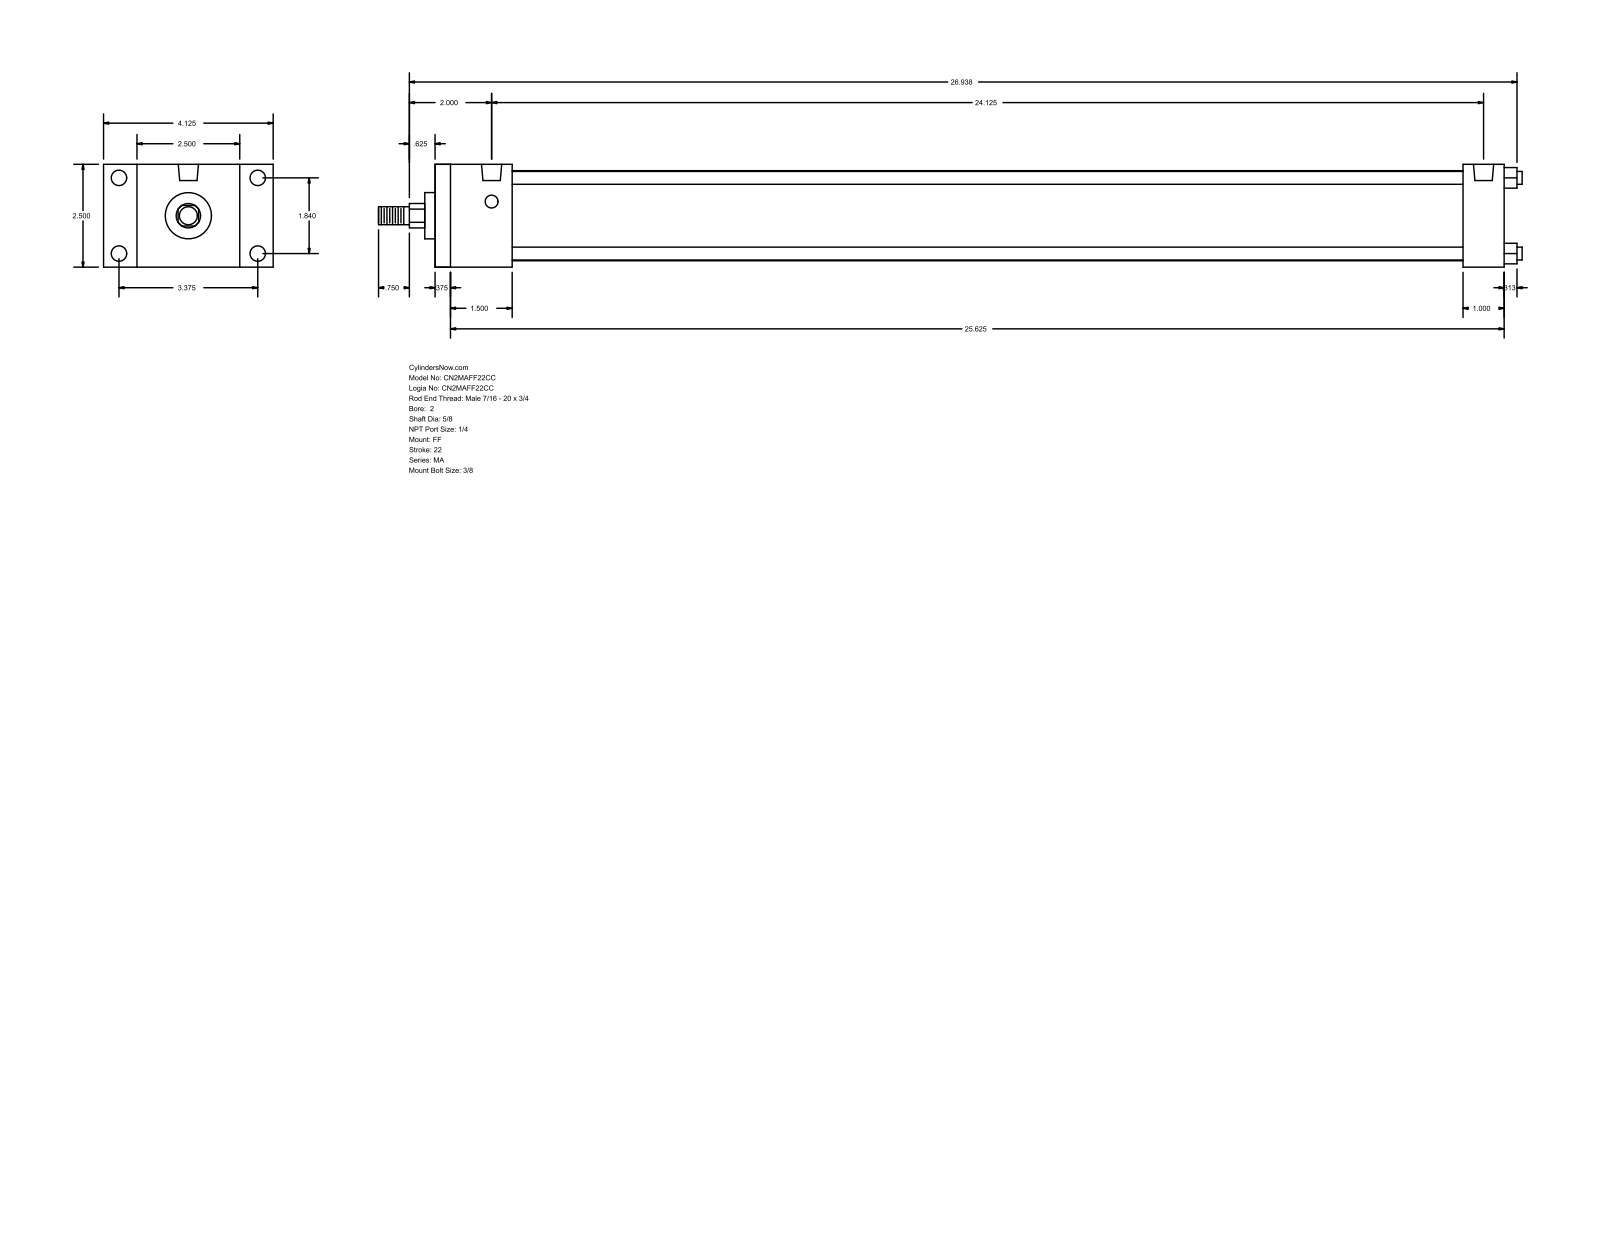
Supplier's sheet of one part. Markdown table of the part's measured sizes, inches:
| quantity | value |
| --- | --- |
| part name | MA_FF__0200_0.625 |
| STEP written by | GSSL Pune (CONFIG_CONTROL_DESIGN) |
| units | inches |
| bodies | 0 solids, 92 faces (64 planar, 28 cylindrical, 0 other) |
| overall size | 27.813 × 4.125 × 2.5 |
| round holes (diameter × count) | 0.313 × 4, 0.375 × 4, 0.492 × 2 |
| round bosses / shafts (diameter × count) | 0.313 × 4, 2.19 × 1, 1.125 × 1, 0.625 × 1, 0.437 × 1 |
| partial cylindrical surfaces (radius × count) | 0.297 × 1 |
| main face-to-face distances | 2.5, 26, 0.375, 25.625, 1.5, 1.875, 25, 24.625, 23.125, 24.125 |
| hole center spacings | 1.84, 3.375, 3.844, 24.125 |
